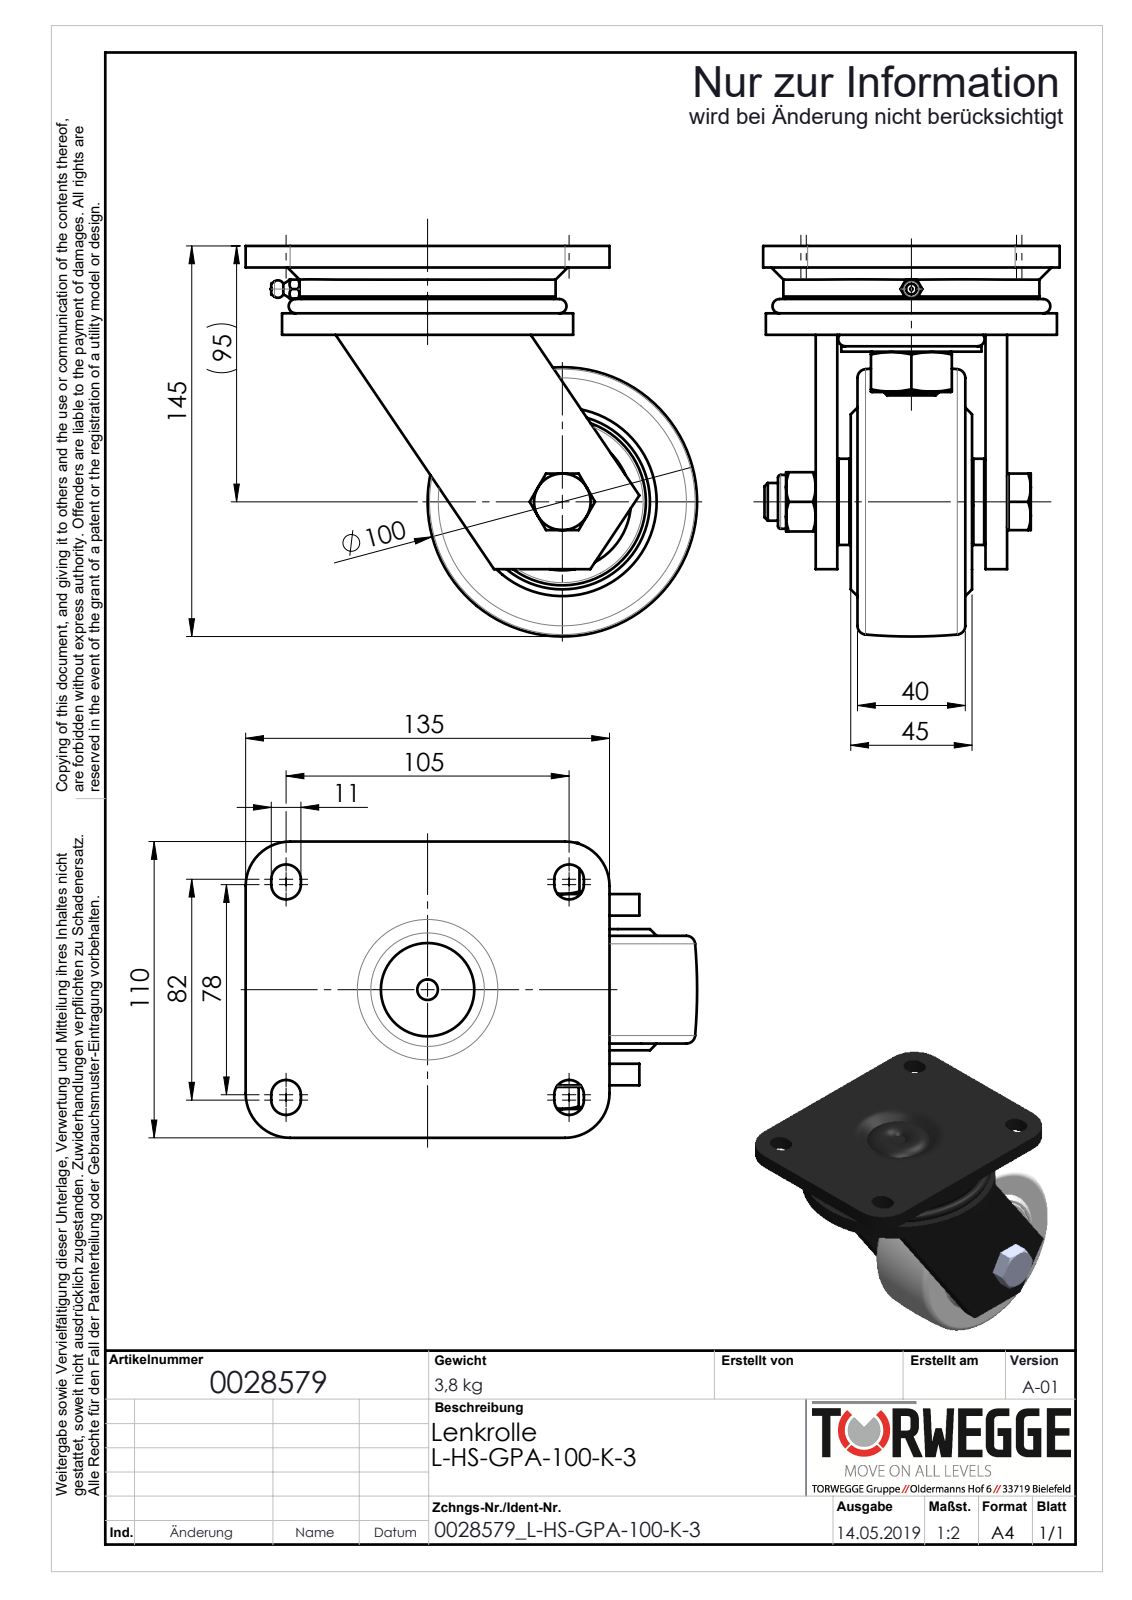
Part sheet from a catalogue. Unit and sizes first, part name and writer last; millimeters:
Units: millimetres
Overall size (bounding box): 167.5 × 145 × 110
Round holes (diameter × count): ⌀5 ×1, ⌀11.84 ×1, ⌀14 ×1, ⌀14.5 ×1, ⌀23 ×1, ⌀25 ×1, ⌀26 ×1, ⌀50.9 ×1, ⌀62 ×1, ⌀95 ×1
Round bosses / shafts (diameter × count): ⌀20 ×2, ⌀108 ×1, ⌀91.4 ×1, ⌀52 ×1, ⌀36.1 ×1, ⌀32 ×1, ⌀6 ×1
Partial cylindrical surfaces — rounded edges, fillets, slot ends (radius × count): R5.5 ×8, R16.5 ×4
Main face-to-face distances: 8, 33, 25, 63, 55, 7.5, 47.5, 55.5, 71, 15.5
Bodies: 0 solids, 290 faces (91 planar, 79 cylindrical, 120 other)
Part name (STEP PRODUCT): 0028579_L-HS-GPA-100-K-3_(A-01)
STEP written by: SolidWorks 2018 (AUTOMOTIVE_DESIGN)
